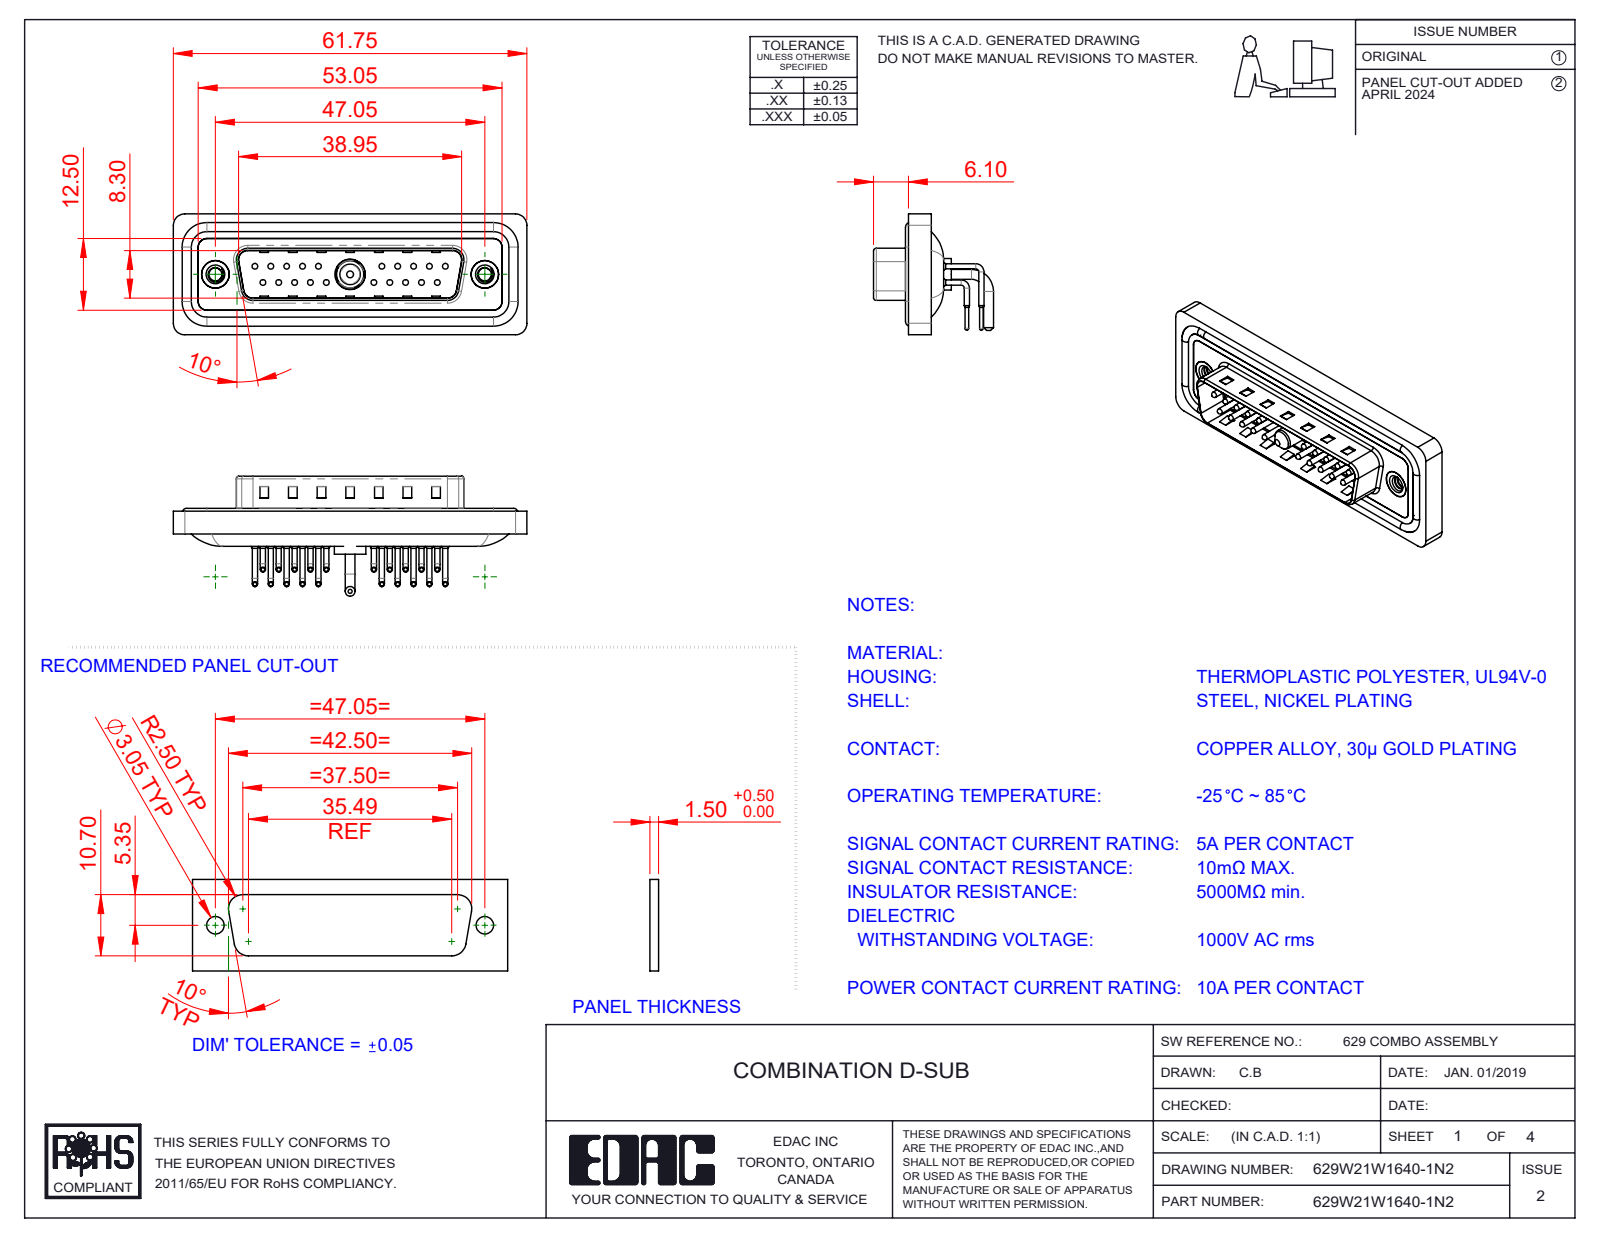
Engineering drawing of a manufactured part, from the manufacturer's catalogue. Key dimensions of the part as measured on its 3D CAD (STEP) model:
Part name (STEP PRODUCT): 629Combo Contact Row 1; 629Combo Shell Front_25 Contacts; Power Pin_10A RA; 629Combo Housing_21W1 (+5 more)
STEP written by: SolidWorks 2023 (CONFIG_CONTROL_DESIGN)
Units: millimetres
Bodies: 29 solids, 2726 faces (1499 planar, 929 cylindrical, 298 other)
Overall size (bounding box): 61.75 × 21.1 × 20.95
Volume: 7 371 mm³ · Surface area: 12 670 mm²
Round holes (diameter × count): ⌀0.75 ×20, ⌀1.6 ×20, ⌀2 ×20, ⌀2.26 ×2, ⌀4 ×2, ⌀4.8 ×2, ⌀5 ×2, ⌀4.85 ×1, ⌀5.3 ×1
Round bosses / shafts (diameter × count): ⌀0.9 ×40, ⌀1.5 ×20, ⌀1 ×20, ⌀0.65 ×20, ⌀1.6 ×4, ⌀4.9 ×2, ⌀1.7 ×2, ⌀5.5 ×1
Partial cylindrical surfaces — rounded edges, fillets, slot ends (radius × count): R1.01 ×20, R1.5 ×18, R2 ×18, R0.5 ×8, R1.6 ×8, R0.25 ×4, R0.6 ×4, R0.65 ×4
Main face-to-face distances: 0.4, 2.9, 0.8, 4.1, 1.1, 2.1, 1.6, 4.5, 1.5, 2.5
Hole centre spacings: 3.16, 2.77, 5.54, 8.31, 5.04, 19.39, 20.97, 22.16
